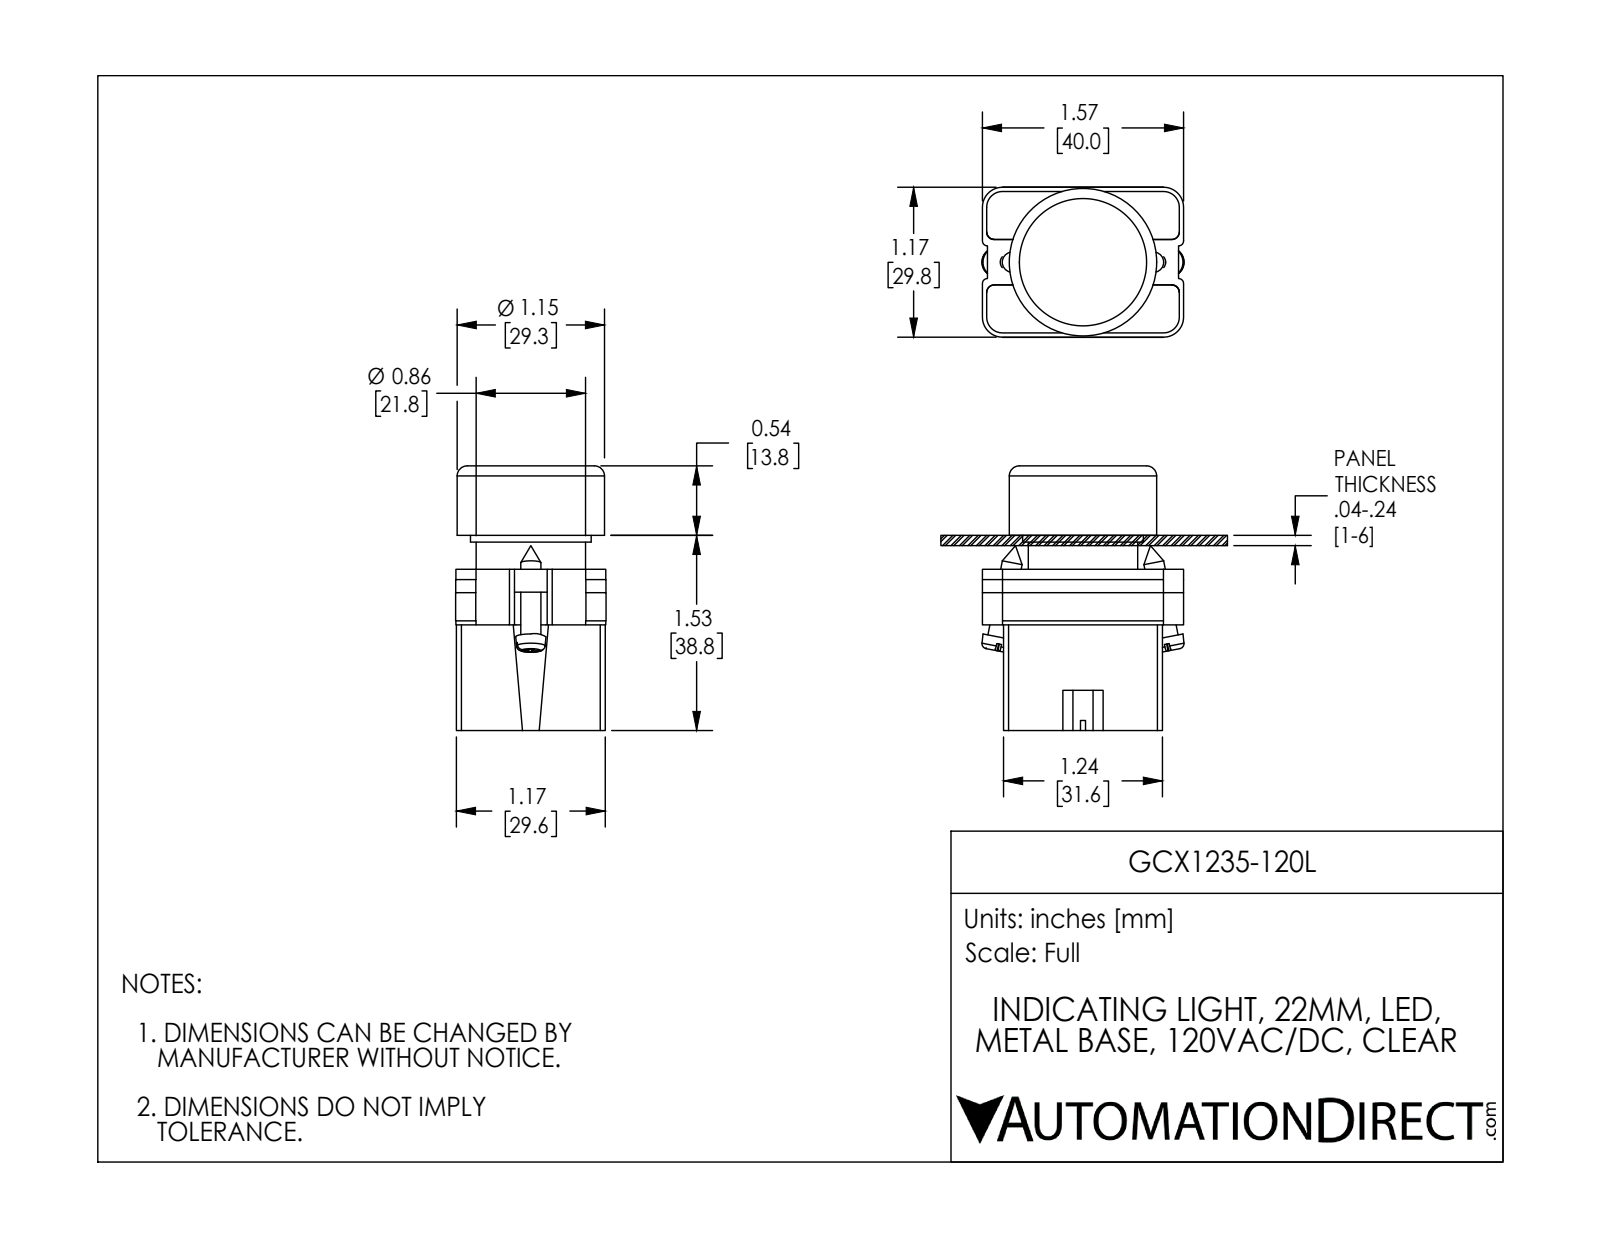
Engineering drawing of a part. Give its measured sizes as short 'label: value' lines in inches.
name: ecx1029; GCX1235-120L; GCX1235L OPERATOR; ECX1050
written by: SolidWorks 2016 (AUTOMOTIVE_DESIGN)
unit: in
bodies: 7 solids, 339 faces (178 planar, 134 cylindrical, 27 other)
size: 2.071 × 1.581 × 1.177
volume: 2.268 in³; area: 31.19 in²
holes: 2× ⌀0.124, 2× ⌀0.13, 1× ⌀0.197, 1× ⌀0.469, 1× ⌀0.852, 1× ⌀0.878, 1× ⌀0.888, 1× ⌀1.102
bosses: 4× ⌀0.157, 1× ⌀1.154, 1× ⌀1.092, 1× ⌀0.945, 1× ⌀0.856, 1× ⌀0.78, 1× ⌀0.504
rounds: 24× R0.059, 12× R0.041, 12× R0.124, 12× R0.157, 8× R0.039, 2× R0.128, 1× R0.392, 1× R0.398
face distances: 0.86, 1.244, 0.827, 1.687, 1.136, 0.033, 1.963, 0.276, 0.031, 1.165
